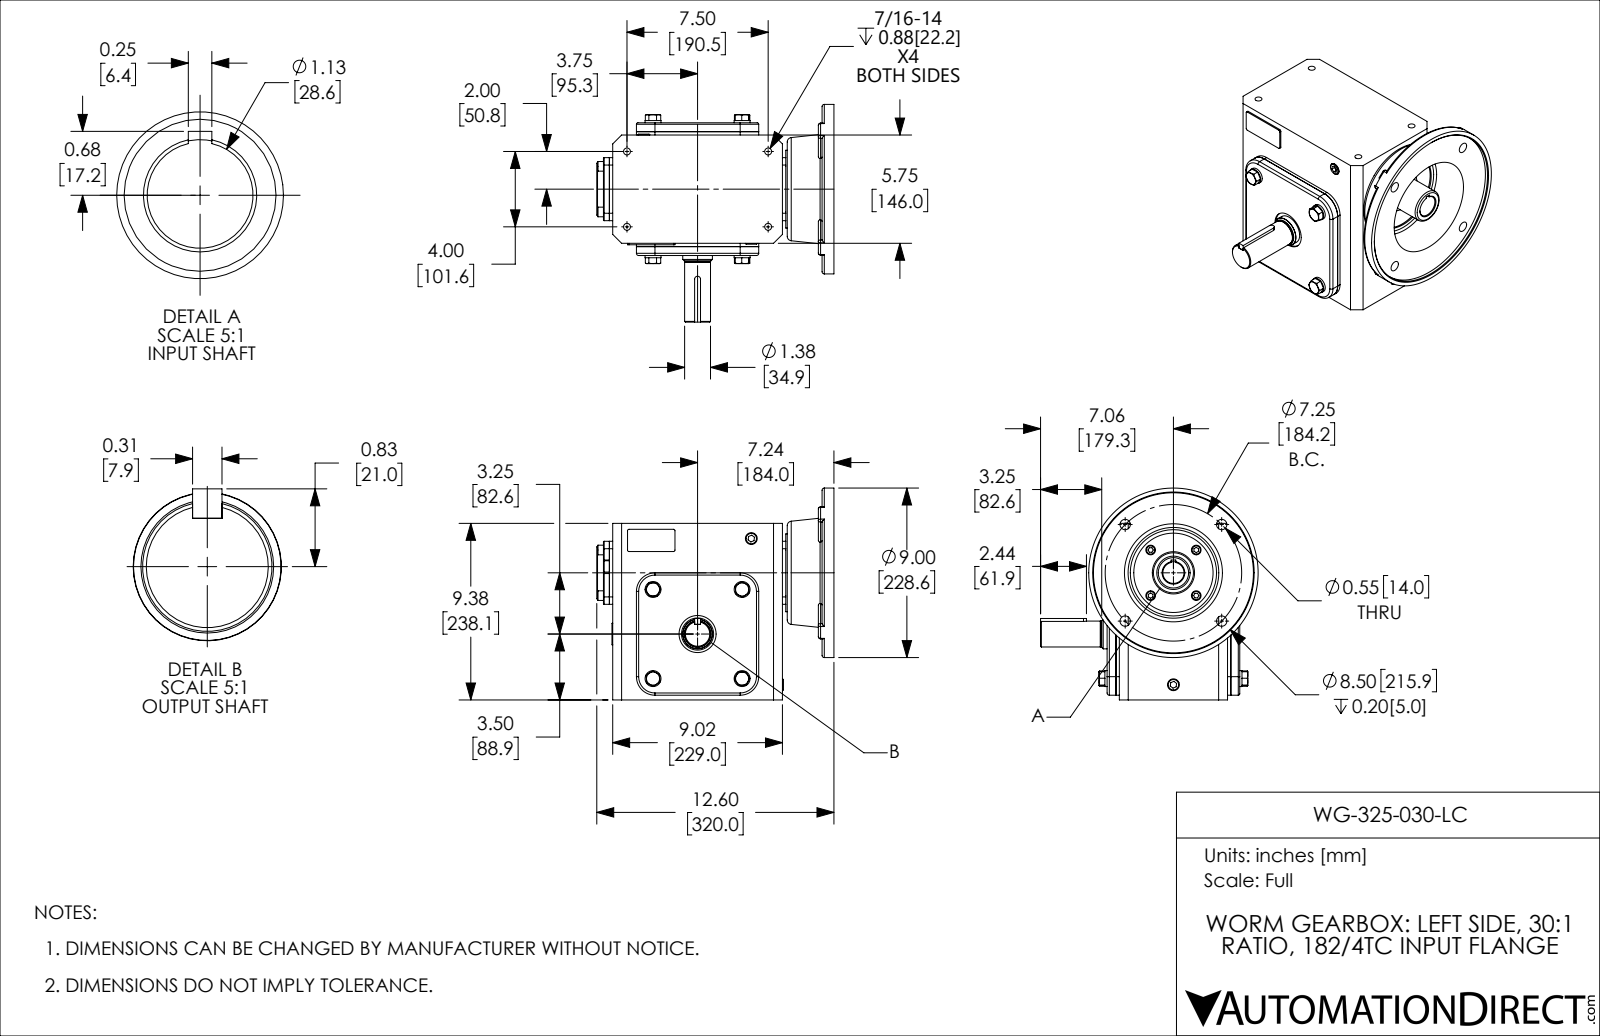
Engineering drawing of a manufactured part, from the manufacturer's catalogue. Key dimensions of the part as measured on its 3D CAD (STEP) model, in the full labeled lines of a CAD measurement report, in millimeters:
Part name (STEP PRODUCT): WG-325-030-LC
STEP written by: SolidWorks 2017 (AUTOMOTIVE_DESIGN)
Units: millimetres
Bodies: 40 solids, 653 faces (336 planar, 195 cylindrical, 122 other)
Overall size (bounding box): 320 × 293.6 × 285.8
Volume: 8 680 000 mm³ · Surface area: 661 900 mm²
Round holes (diameter × count): ⌀9 ×4, ⌀9.3 ×4, ⌀14 ×4, ⌀16 ×3, ⌀15 ×1, ⌀24.8 ×1, ⌀28.6 ×1, ⌀30 ×1, ⌀50 ×1, ⌀57 ×1, ⌀62 ×1, ⌀70 ×1
Round bosses / shafts (diameter × count): ⌀21.5 ×4, ⌀13 ×4, ⌀228.6 ×1, ⌀105 ×1, ⌀72 ×1, ⌀45 ×1, ⌀40 ×1, ⌀34.9 ×1
Partial cylindrical surfaces — rounded edges, fillets, slot ends (radius × count): R3 ×14, R2 ×11, R10 ×4, R23 ×4, R25 ×4, R0.5 ×2, R1 ×2, R4 ×1
Main face-to-face distances: 2, 4.5, 165, 10, 177, 12, 167, 162.5, 14.5, 16.5
Hole centre spacings: 101.8, 43.5, 48.6, 61.5, 92.1, 130.2, 135.6, 60.2
